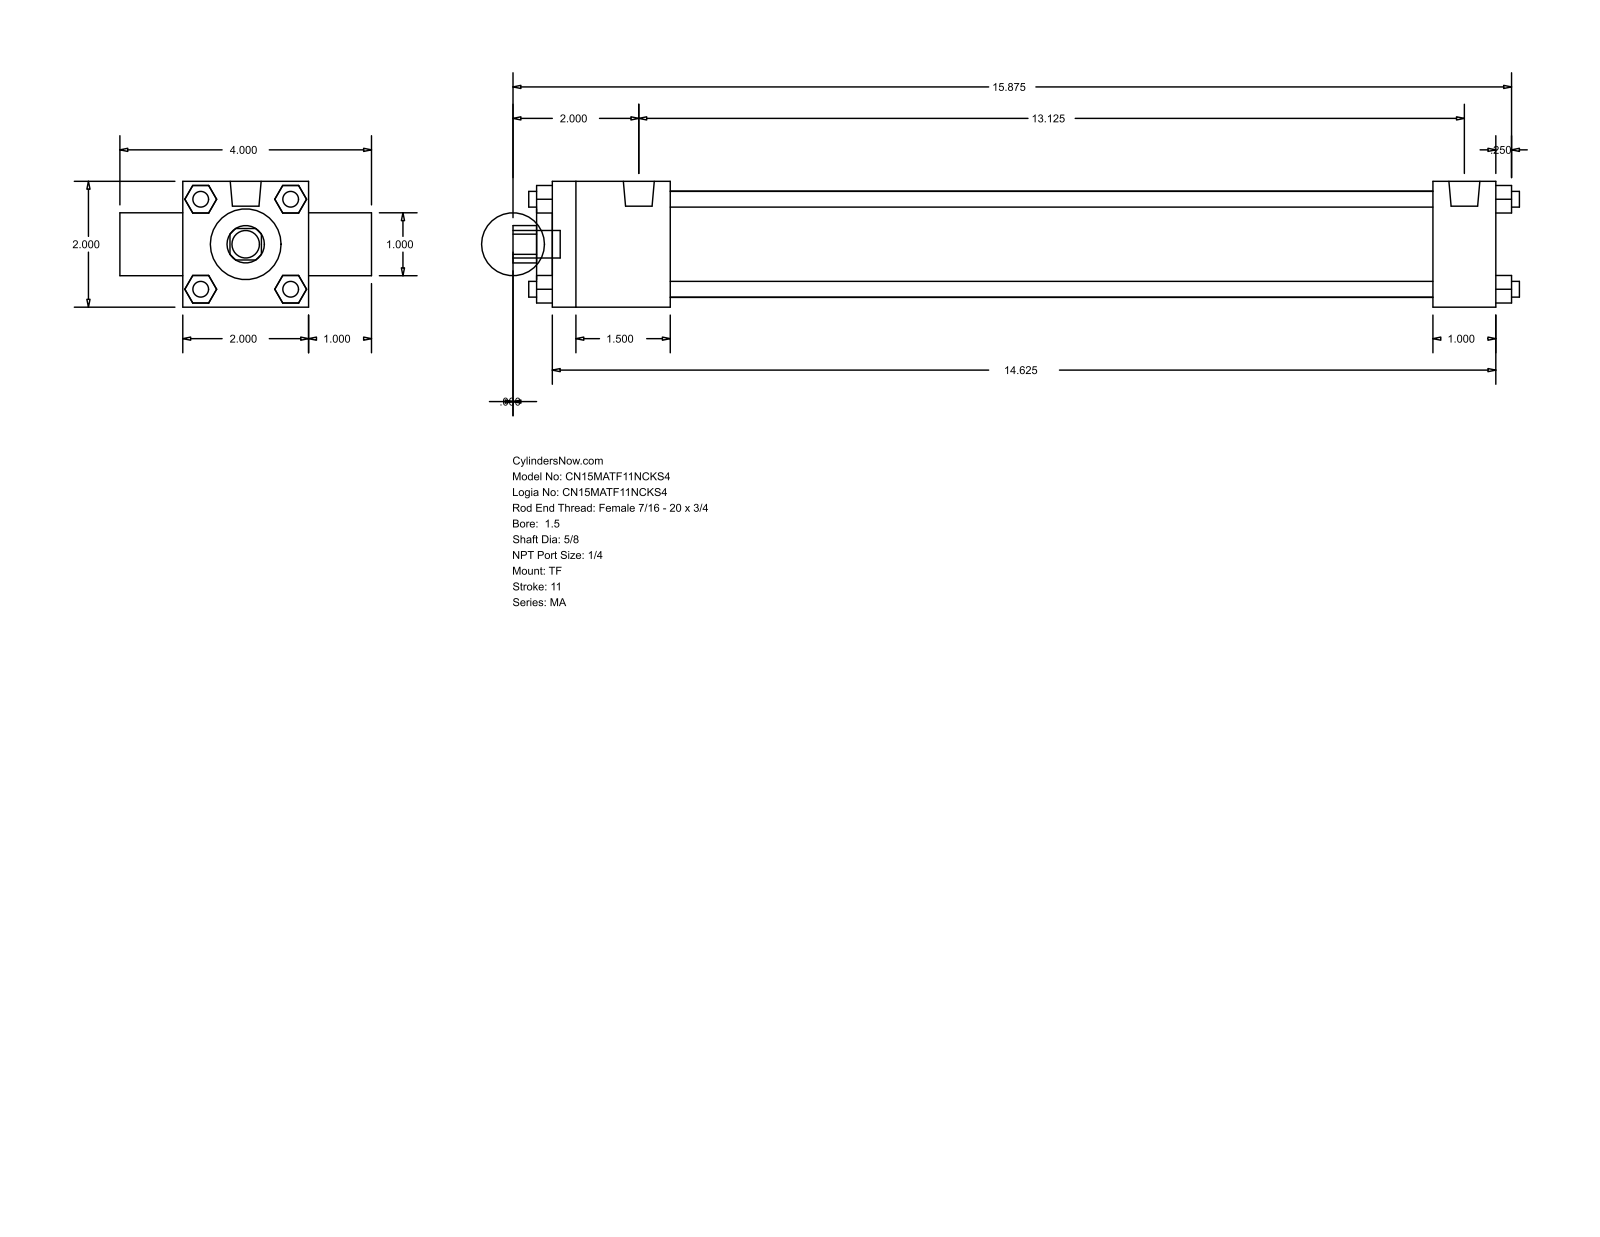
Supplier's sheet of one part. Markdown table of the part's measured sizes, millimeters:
| quantity | value |
| --- | --- |
| part name | MA_TF__0150_0.625 |
| STEP written by | GSSL Pune (CONFIG_CONTROL_DESIGN) |
| units | millimeters |
| bodies | 0 solids, 120 faces (92 planar, 28 cylindrical, 0 other) |
| overall size | 406.4 × 101.6 × 50.8 |
| round holes (diameter × count) | 15.88 × 1, 25.4 × 1, 28.57 × 1, 42.93 × 1 |
| round bosses / shafts (diameter × count) | 6.35 × 4, 7.94 × 3, 12.49 × 2, 11.11 × 1 |
| partial cylindrical surfaces (radius × count) | 7.54 × 1 |
| main face-to-face distances | 50.8, 25.4, 381, 387.35, 6.35, 76.2, 47.62, 355.6, 307.98, 333.38 |
